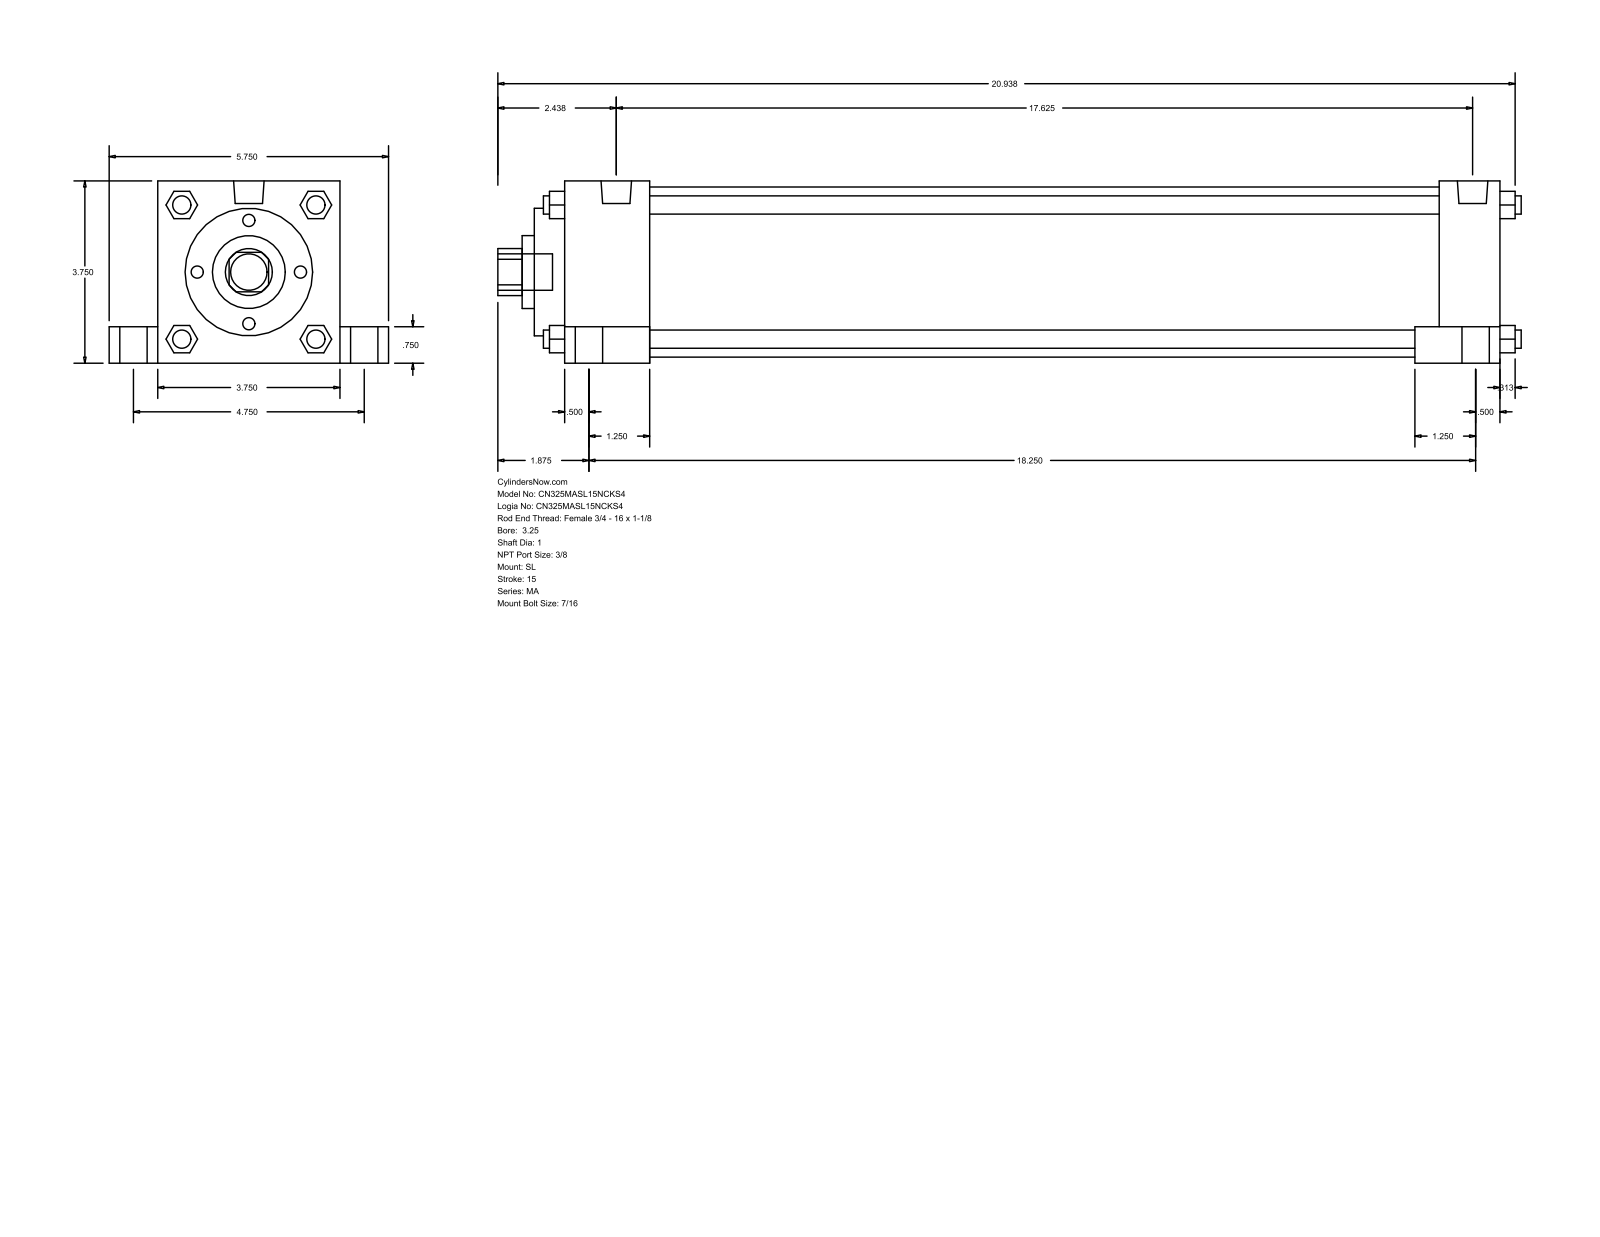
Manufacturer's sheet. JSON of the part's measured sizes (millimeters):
{"part_name": "MA_SL__0325_1", "step_written_by": "GSSL Pune (CONFIG_CONTROL_DESIGN)", "units": "millimeters", "bodies": {"solids": 0, "faces": 150, "planar": 113, "cylindrical": 37, "other": 0}, "overall_size": [534.99, 146.05, 95.25], "round_holes": [[25.4, 1], [38.1, 1], [66.67, 1], [88.9, 1]], "round_bosses_or_shafts": [[20.64, 4], [14.29, 4], [11.11, 4], [9.53, 4], [15.93, 2], [19.05, 1]], "partial_cylinders_radius": [[12.29, 1]], "face_to_face_distances": [95.24, 488.96, 15.87, 25.41, 120.65, 19.05, 457.2, 31.76, 44.46, 412.74]}
